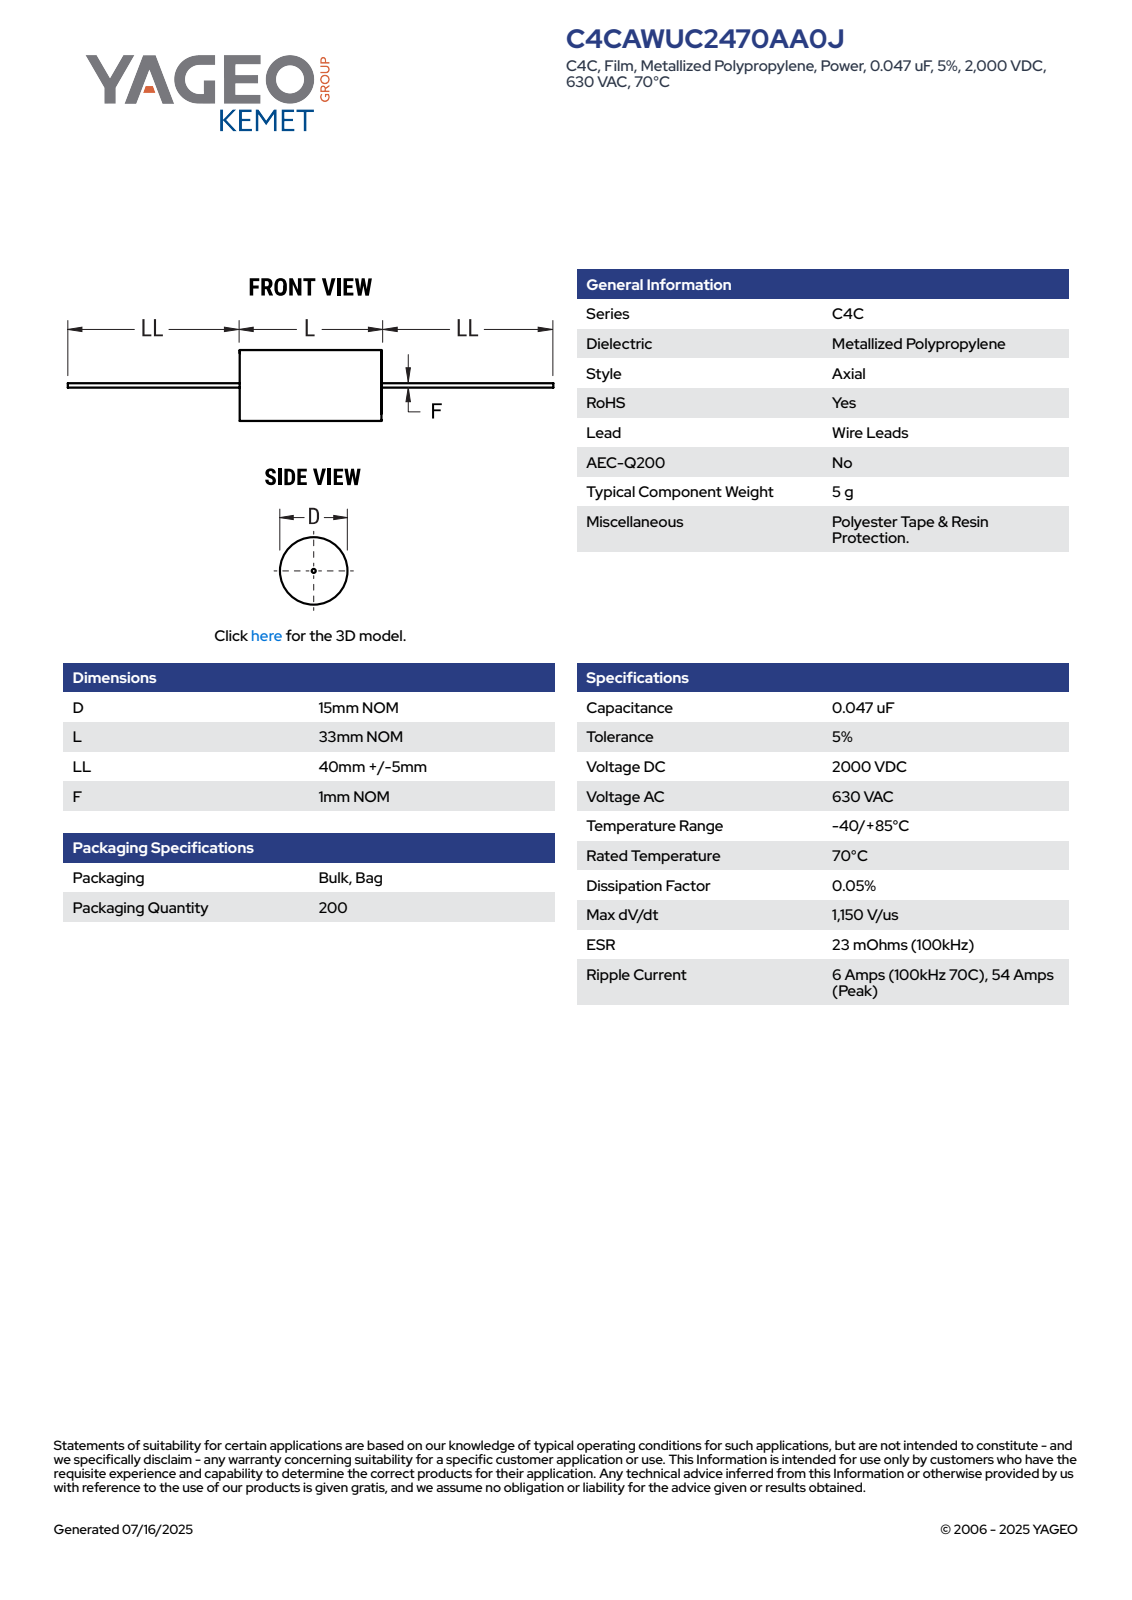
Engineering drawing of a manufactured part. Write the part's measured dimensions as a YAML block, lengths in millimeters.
part_name: "CFP_ACWF_15X33_D15L33LL45F1"
step_written_by: "SolidWorks 2014 (AUTOMOTIVE_DESIGN)"
units: millimeters
bodies: {solids: 2, faces: 87, planar: 28, cylindrical: 28, other: 31}
overall_size: [123, 15, 15]
volume: 5902
surface_area: 2544
round_bosses_or_shafts:
  - {diameter: 15, count: 1}
  - {diameter: 1, count: 1}
partial_cylinders:
  - {radius: 7.49, count: 1}
face_to_face_distances: [33.01, 33, 45, 78, 44.99, 123, 78.01]
